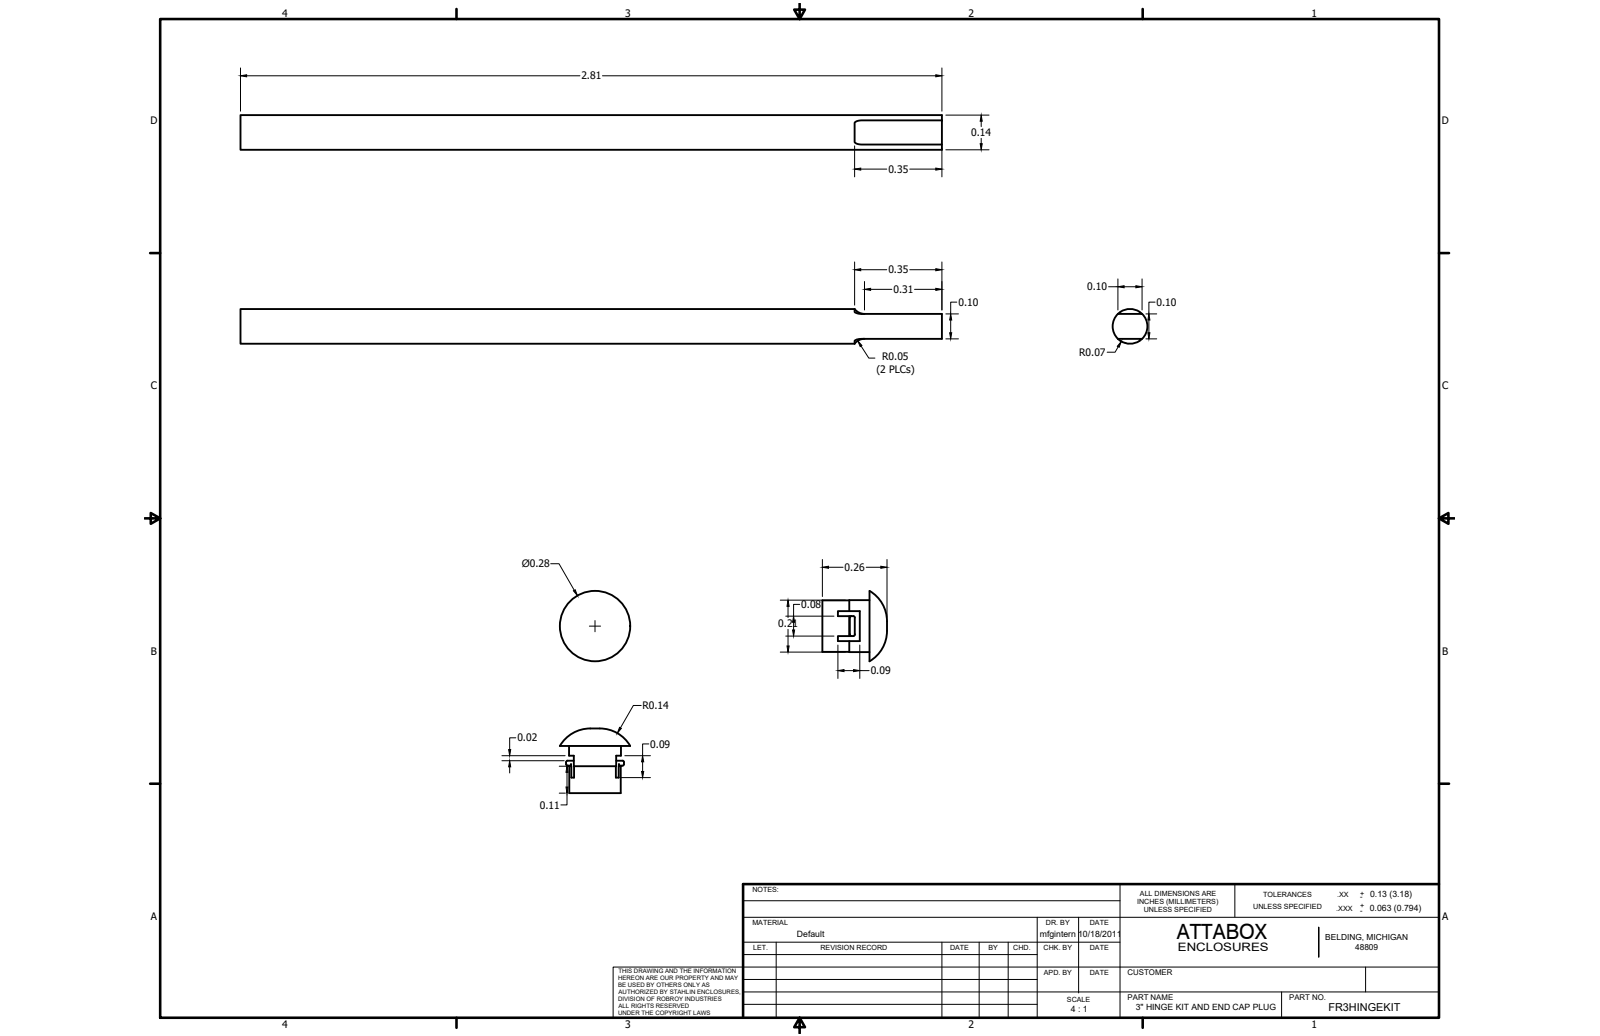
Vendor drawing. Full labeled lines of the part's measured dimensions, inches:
Part name (STEP PRODUCT): FR3HINGEKIT
STEP written by: SolidWorks 2019 (AUTOMOTIVE_DESIGN)
Units: inches
Bodies: 6 solids, 252 faces (136 planar, 86 cylindrical, 30 other)
Overall size (bounding box): 3.632 × 2.053 × 1.389
Volume: 0.102 in³ · Surface area: 3.876 in²
Round holes (diameter × count): ⌀0.131 ×4
Round bosses / shafts (diameter × count): ⌀0.208 ×4, ⌀0.206 ×4, ⌀0.135 ×2
Partial cylindrical surfaces — rounded edges, fillets, slot ends (radius × count): R0.006 ×32, R0.008 ×12, R0.401 ×4
Main face-to-face distances: 0.093, 0.096, 0.189, 0.598, 0.595, 0.502, 0.115, 0.343, 0.02, 0.1
Hole centre spacings: 0.407, 0.522, 0.831, 0.859, 1.093, 1.499
